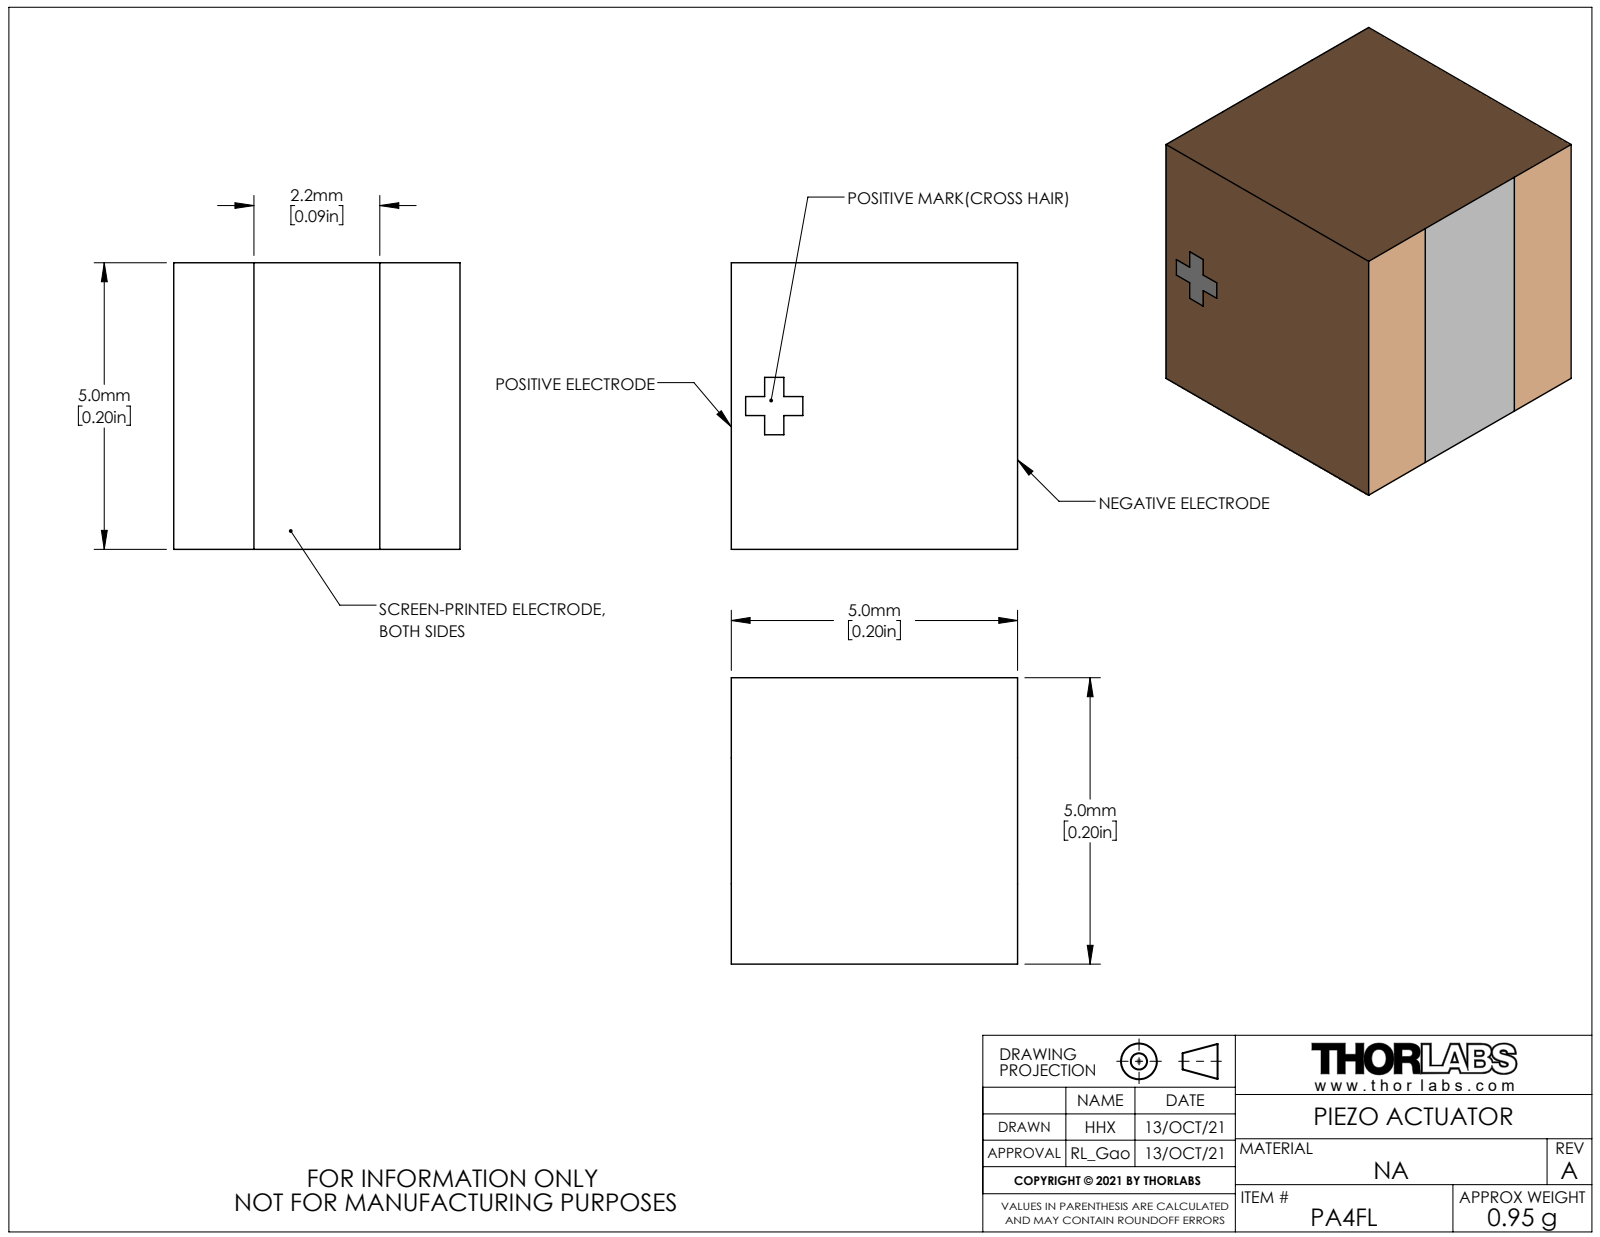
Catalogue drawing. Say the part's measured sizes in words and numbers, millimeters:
The part is named "PA4FL". Its 3-D file was written by "SolidWorks 2019 (AUTOMOTIVE_DESIGN)". It is 1 solid with 11 faces: 11 planar, 0 cylindrical and 0 other. Overall it measures 5 by 5 by 5 millimeters. Its volume is 125 cubic millimeters and its surface area 150 square millimeters. The main face-to-face distances are 5.
